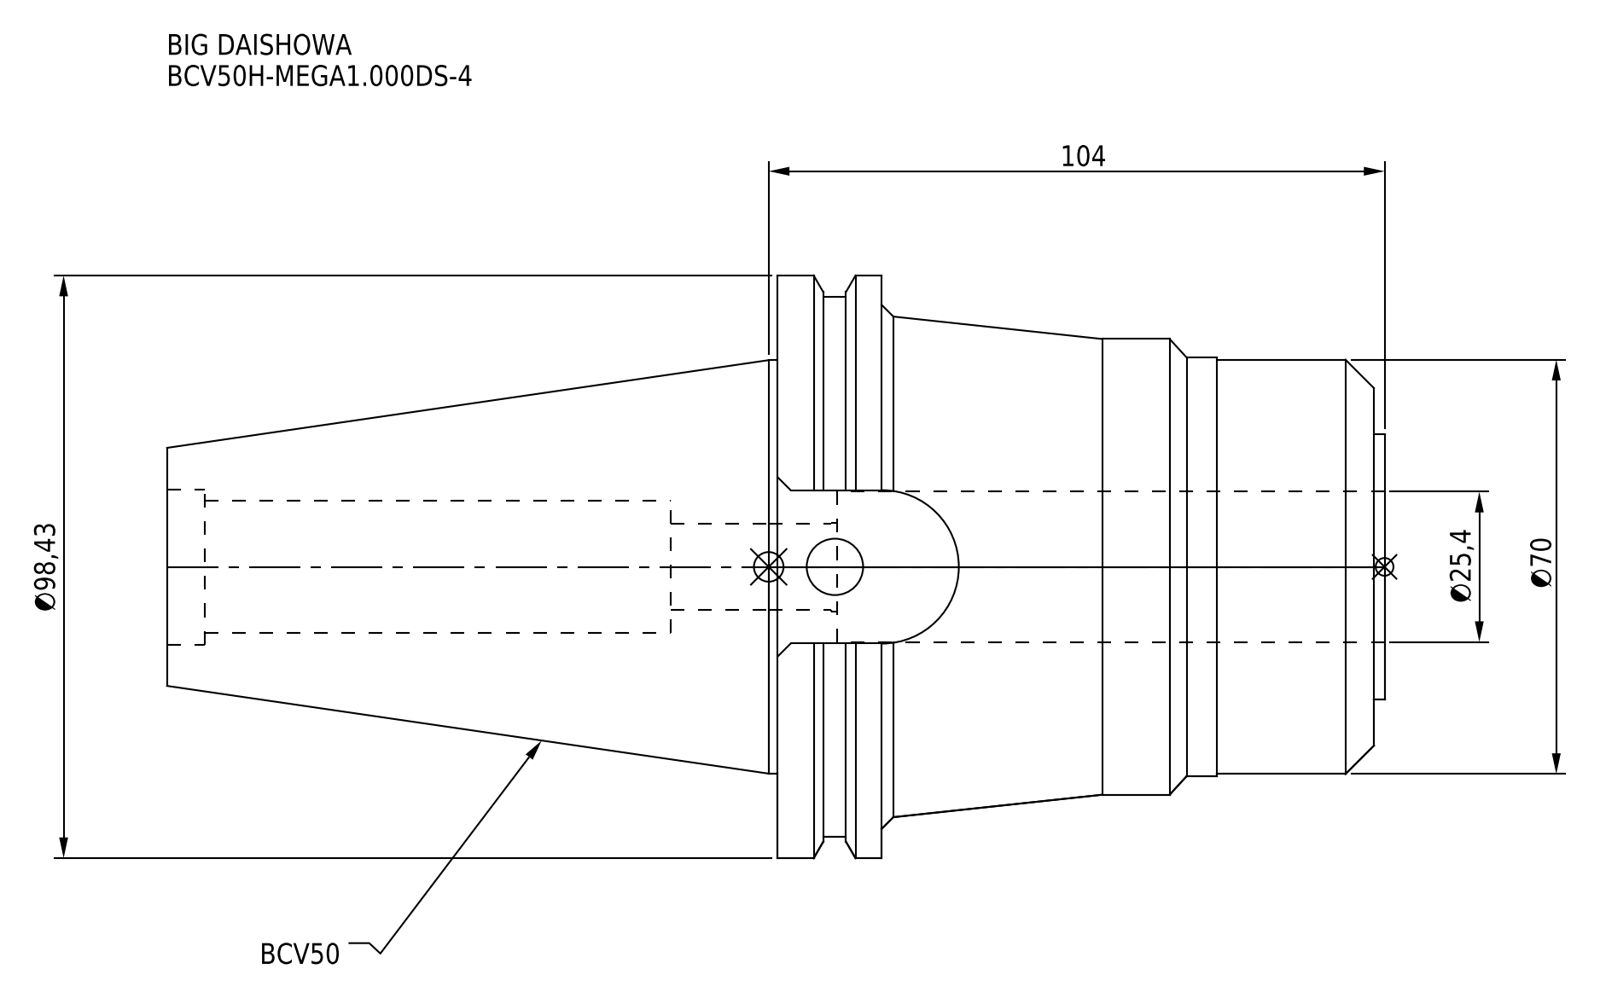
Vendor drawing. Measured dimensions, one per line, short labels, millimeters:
name: BCV50H-MEGA1_000DS-4
written by: CREO PARAMETRIC BY PTC INC, 2016380 (AUTOMOTIVE_DESIGN)
unit: mm
bodies: 1 solid, 72 faces (26 planar, 32 cylindrical, 14 other)
size: 205.6 × 98.42 × 94.95
volume: 663 286 mm³; area: 69 469 mm²
holes: 1× ⌀9.53, 1× ⌀14.5, 1× ⌀15, 1× ⌀22.3, 1× ⌀25.4, 1× ⌀26.23
bosses: 1× ⌀98.42, 1× ⌀91.29, 1× ⌀77, 1× ⌀70.7, 1× ⌀70, 1× ⌀69.85, 1× ⌀44.8
rounds: 1× R12.96
face distances: 100.7, 83.15, 17.55, 1.8, 84.95, 102.5, 205.6, 203.8, 120.65, 103.1
